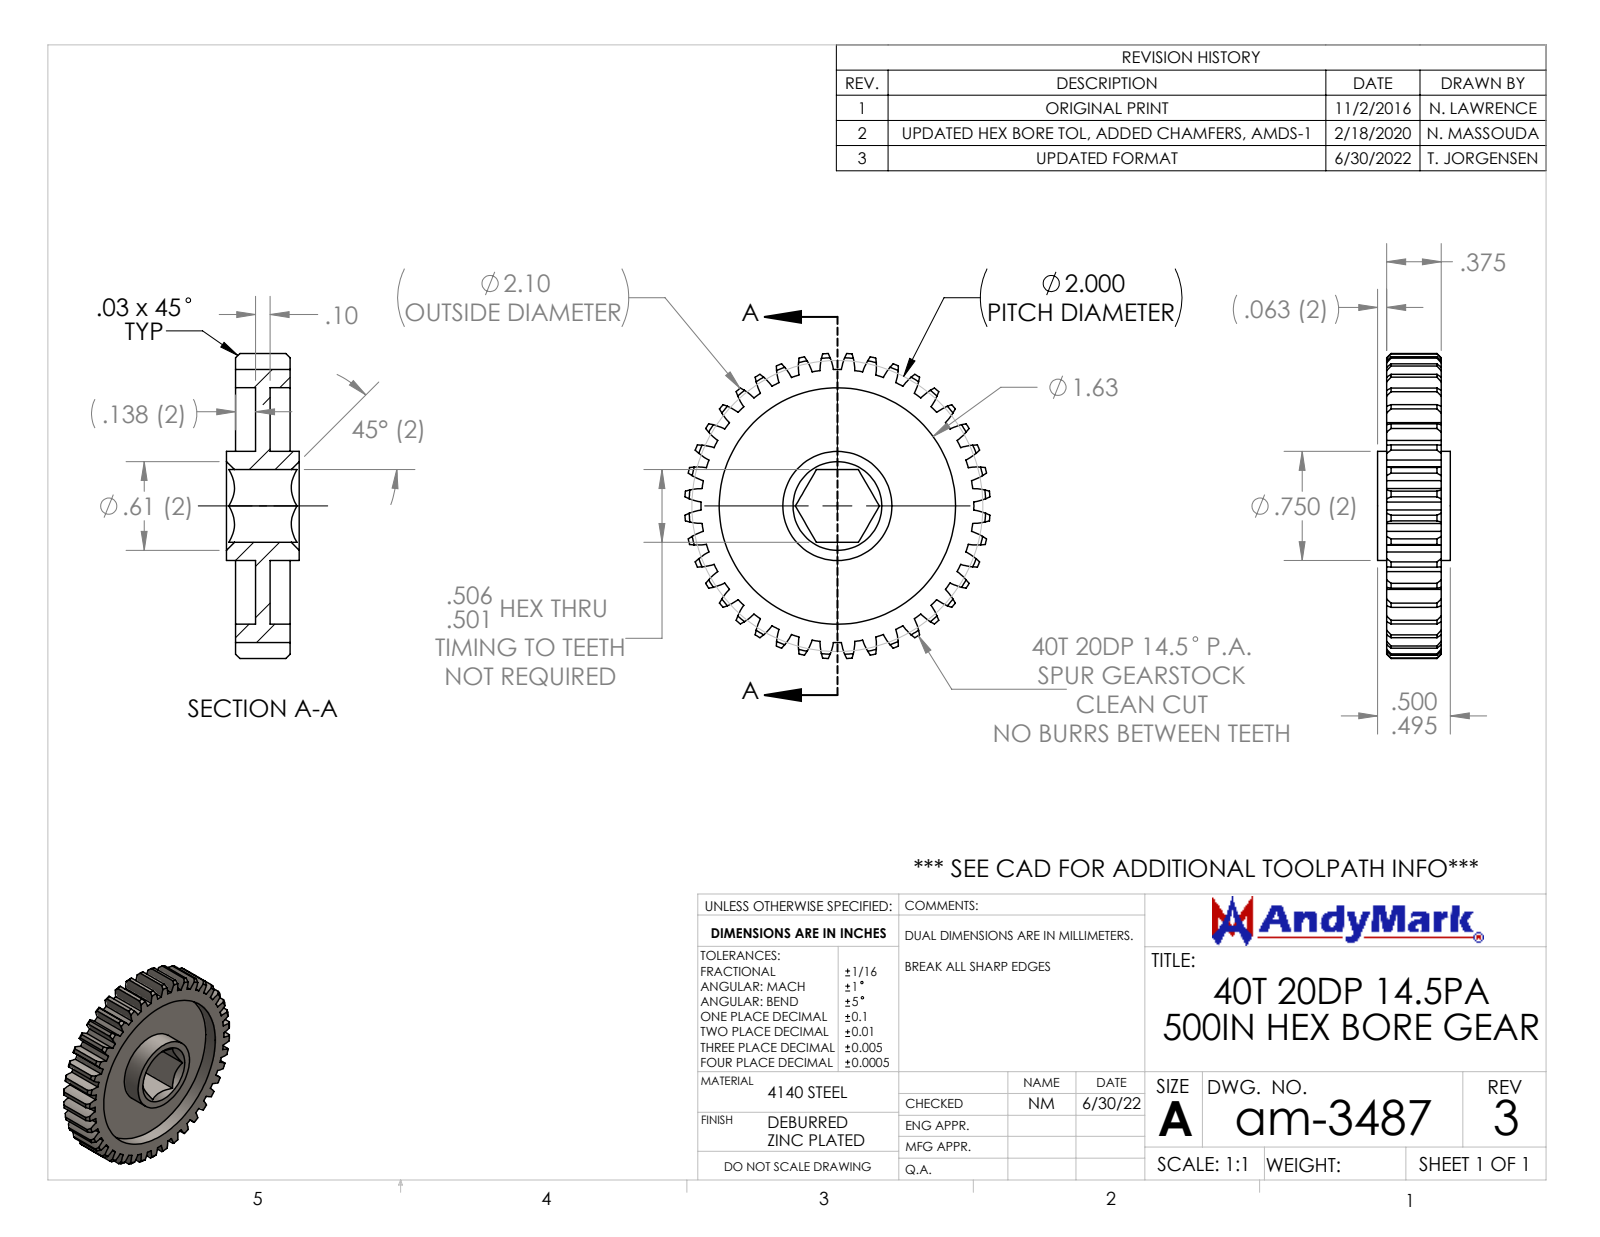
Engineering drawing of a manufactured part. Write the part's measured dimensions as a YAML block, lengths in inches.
part_name: "am-3487 40T 20DP 500hex 375 FW"
step_written_by: "SolidWorks 2022 (CONFIG_CONTROL_DESIGN)"
units: inches
bodies: {solids: 1, faces: 267, planar: 12, cylindrical: 171, other: 84}
overall_size: [2.096, 2.096, 0.5]
volume: 0.65
surface_area: 13.65
round_holes:
  - {diameter: 1.625, count: 1}
round_bosses_or_shafts:
  - {diameter: 0.75, count: 1}
partial_cylinders:
  - {radius: 0.4, count: 80}
  - {radius: 0.938, count: 1}
  - {radius: 1.05, count: 1}
face_to_face_distances: [0.1, 0.137, 0.237, 0.375, 0.238, 0.138, 0.5, 0.2, 0.3, 0.063]
